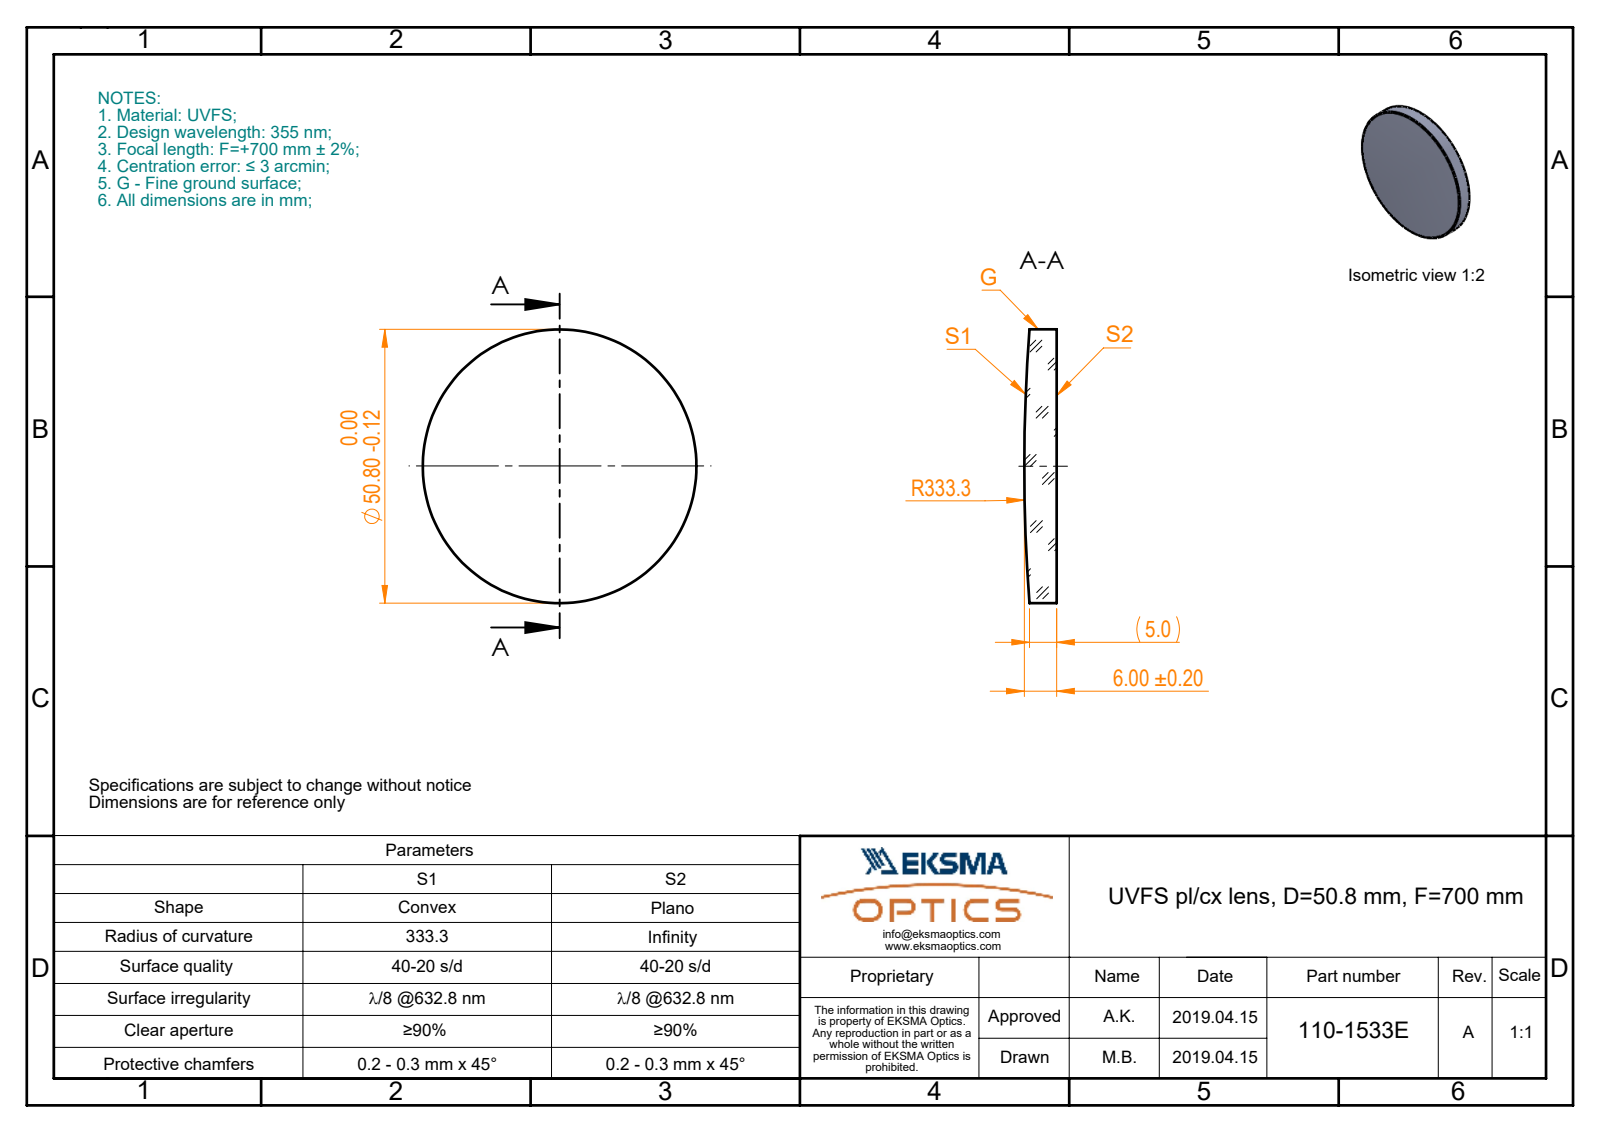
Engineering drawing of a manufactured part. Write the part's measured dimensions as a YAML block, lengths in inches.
part_name: "110-1533E UVFS pl-cx 50.8 F700"
step_written_by: "SolidWorks 2017 (CONFIG_CONTROL_DESIGN)"
units: inches
bodies: {solids: 1, faces: 5, planar: 1, cylindrical: 2, other: 2}
overall_size: [2, 2, 0.236]
volume: 0.682
surface_area: 7.531
round_bosses_or_shafts:
  - {diameter: 2, count: 1}
